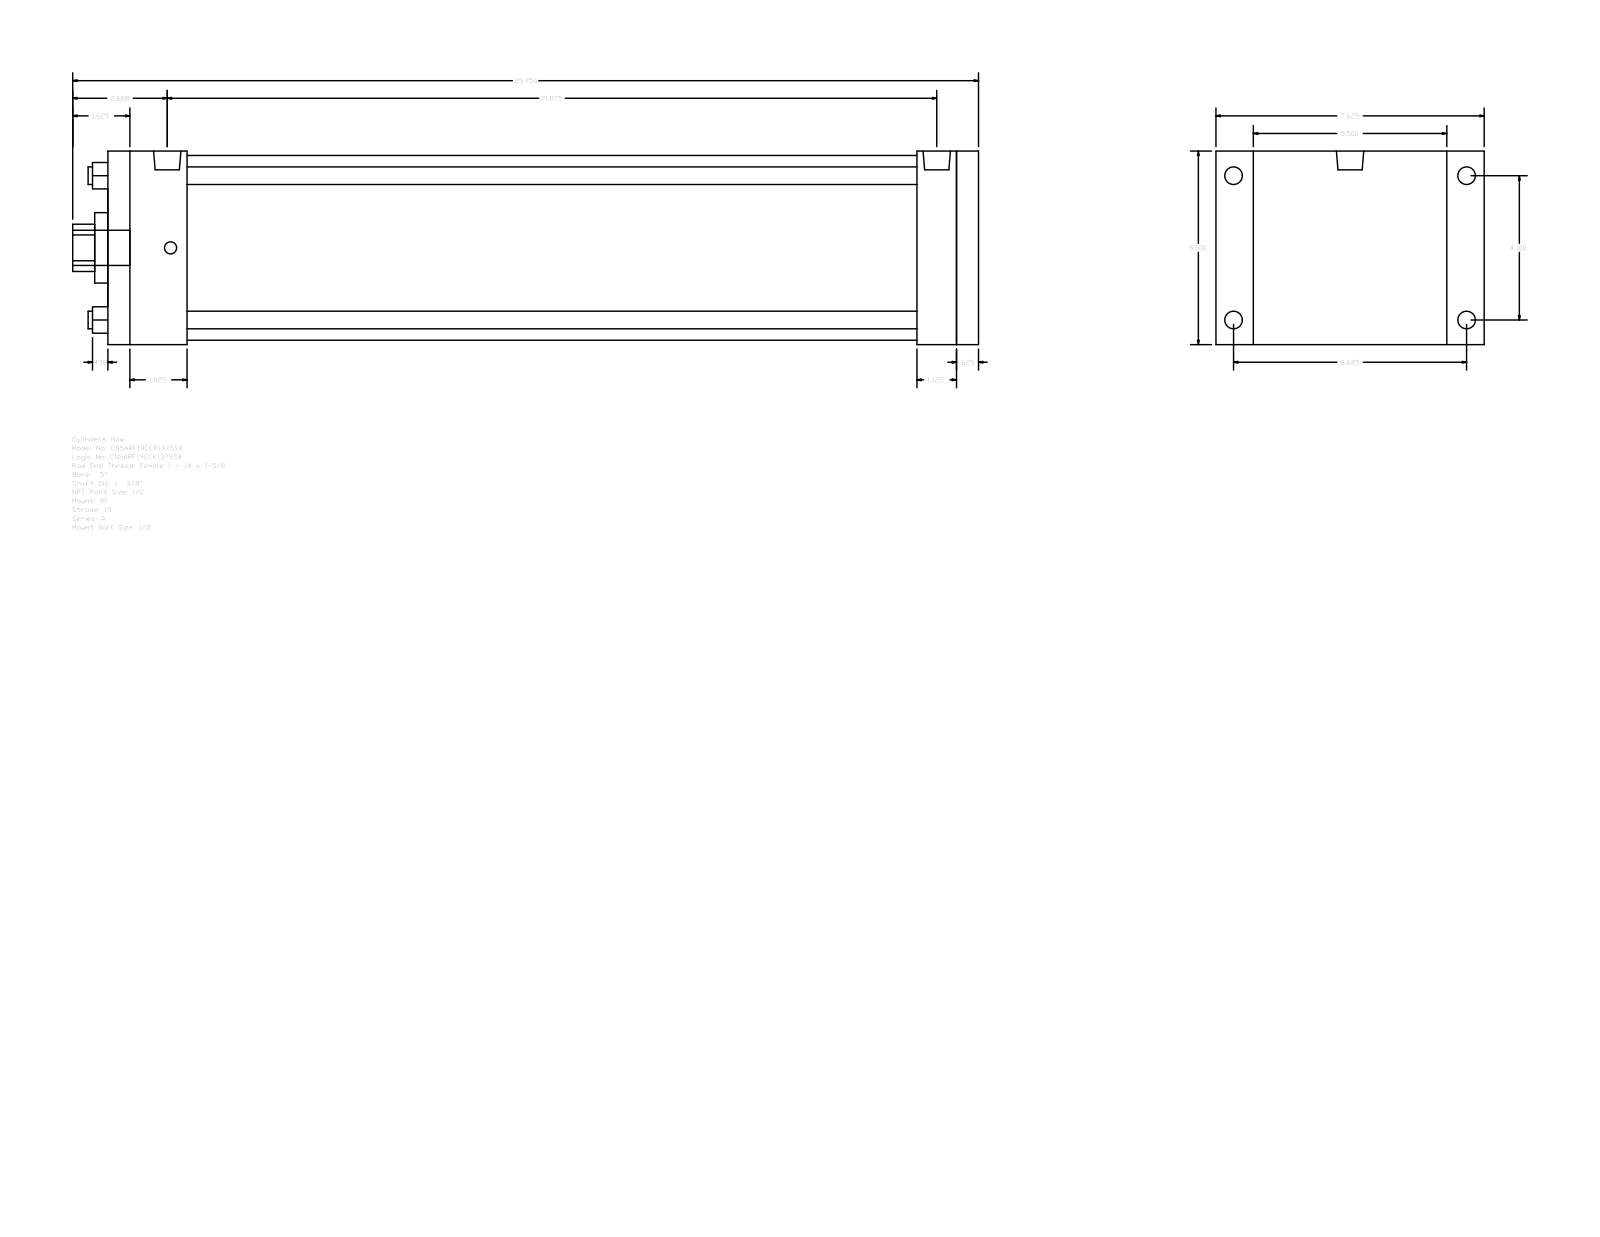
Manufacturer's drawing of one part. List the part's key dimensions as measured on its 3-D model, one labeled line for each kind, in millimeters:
Part name (STEP PRODUCT): A_RF__0500_1.375
STEP written by: GSSL Pune (CONFIG_CONTROL_DESIGN)
Units: millimetres
Bodies: 0 solids, 92 faces (64 planar, 28 cylindrical, 0 other)
Overall size (bounding box): 654.05 × 193.68 × 139.7
Round holes (diameter × count): ⌀12.7 ×4, ⌀34.92 ×1, ⌀50.8 ×1, ⌀133.35 ×1
Round bosses / shafts (diameter × count): ⌀12.7 ×4, ⌀8.73 ×4, ⌀19.77 ×2, ⌀25.4 ×1
Partial cylindrical surfaces — rounded edges, fillets, slot ends (radius × count): R17.06 ×1
Main face-to-face distances: 139.7, 628.65, 15.88, 612.77, 28.57, 57.15, 555.62, 571.5, 584.2, 527.05
Hole centre spacings: 73.64, 104.14, 147.28
